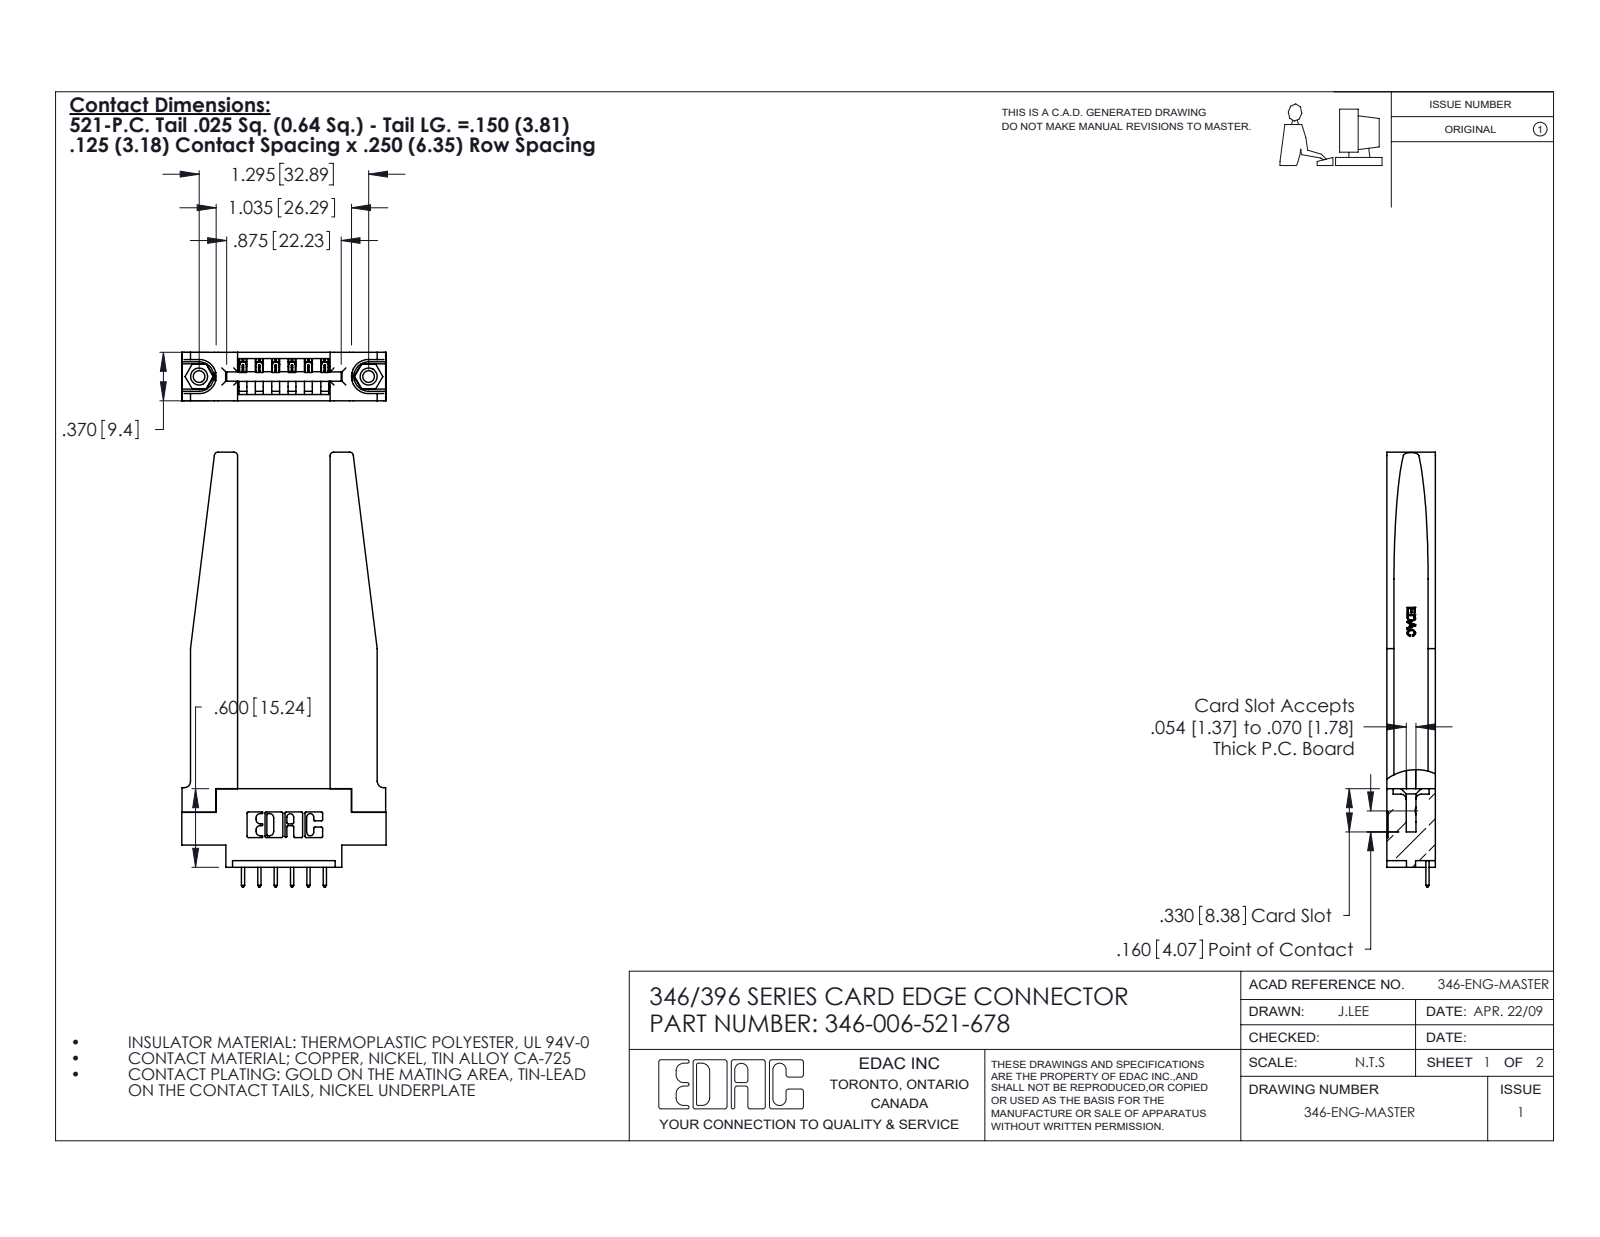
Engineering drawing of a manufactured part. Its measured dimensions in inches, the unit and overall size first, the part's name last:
Units: inches
Overall size (bounding box): 3.32 × 1.56 × 0.37
Round holes (diameter × count): ⌀0.089 ×2, ⌀0.125 ×2, ⌀0.156 ×2, ⌀0.064 ×1
Round bosses / shafts (diameter × count): ⌀0.155 ×2
Partial cylindrical surfaces — rounded edges, fillets, slot ends (radius × count): R0.01 ×22, R0.006 ×12, R0.01 ×12, R0.03 ×8, R0.007 ×6, R0.031 ×6, R0.026 ×3, R0.031 ×2
Main face-to-face distances: 0.37, 0.15, 0.22, 0.706, 0.25, 0.072, 0.148, 0.048, 0.322, 0.102
Hole centre spacings: 0.246, 1.092, 1.295
Volume: 0.626 in³ · Surface area: 16.23 in²
Bodies: 11 solids, 722 faces (476 planar, 194 cylindrical, 52 other)
Part name (STEP PRODUCT): 345-292-001_345-293-121; 346 Part_0.170 Offset - 0.156 Dia-TH; 346-220-078_345-220-078; 346-006-521-678 (+1 more)
STEP written by: SolidWorks 2020 (CONFIG_CONTROL_DESIGN)
